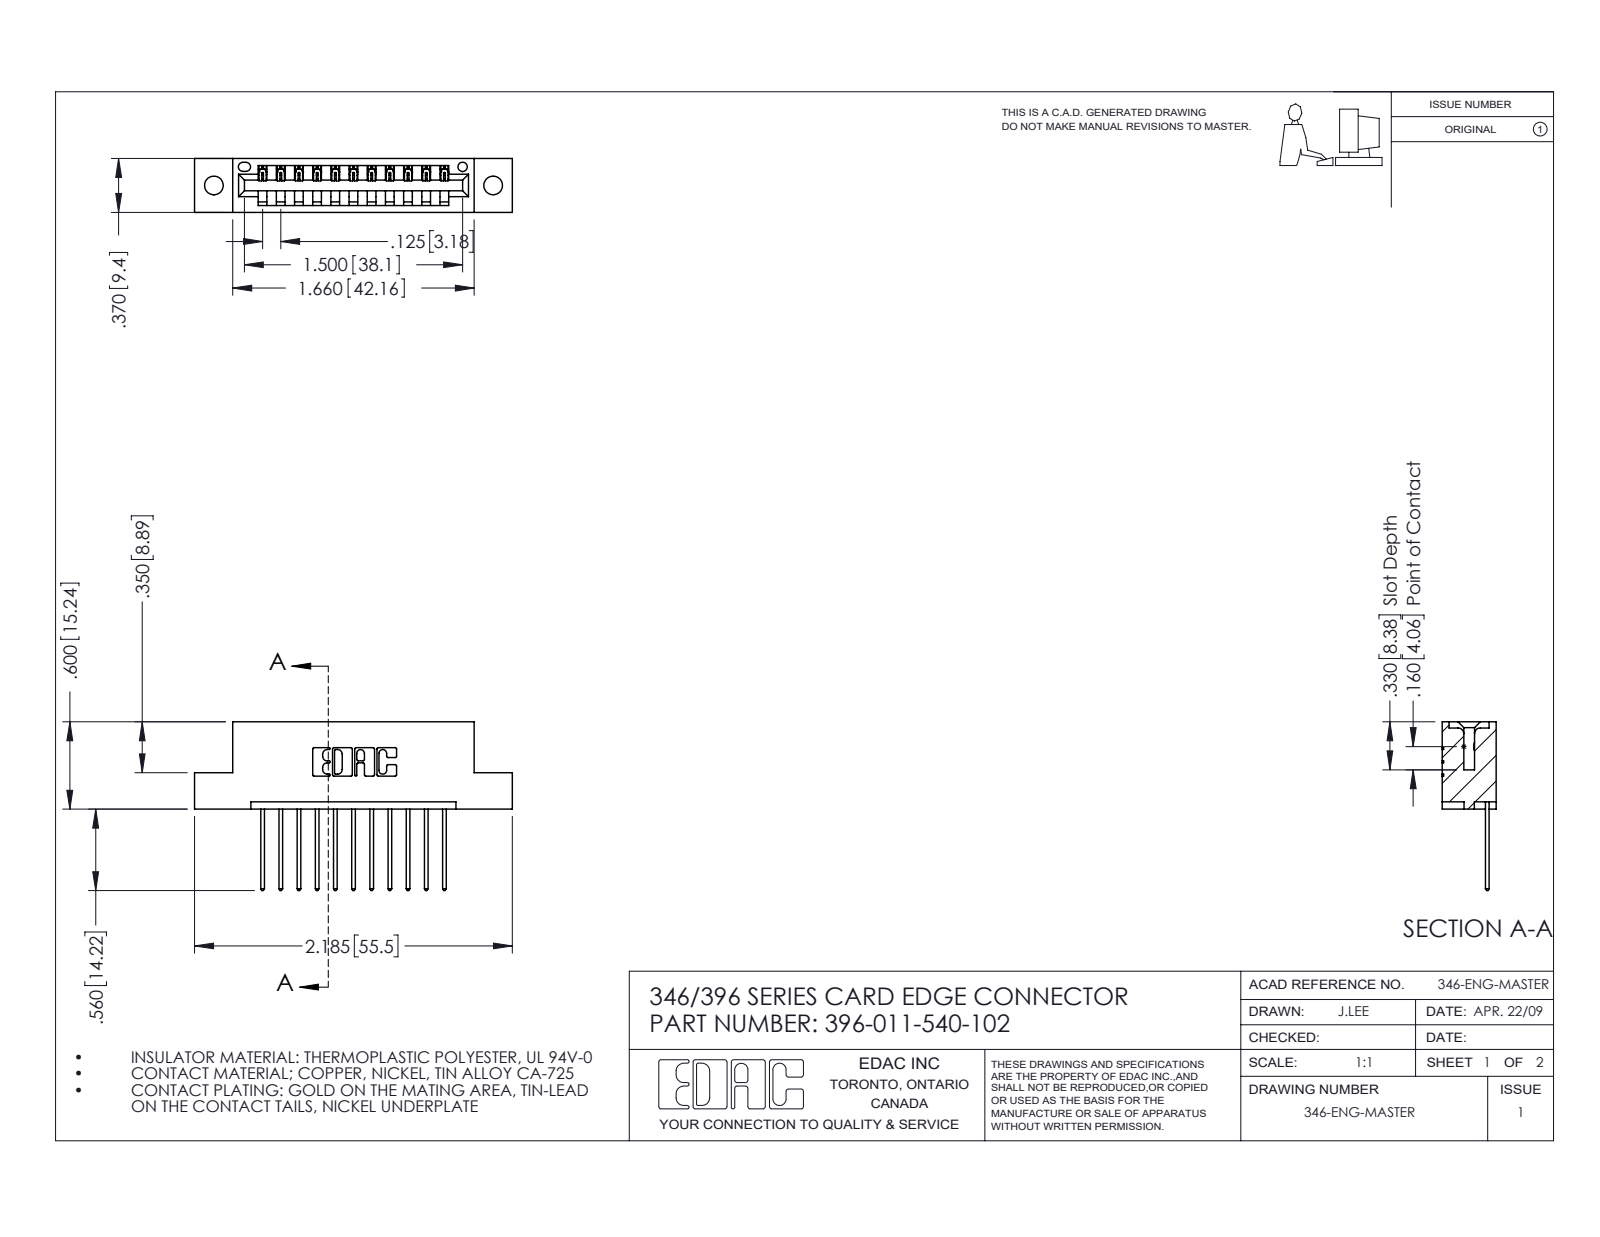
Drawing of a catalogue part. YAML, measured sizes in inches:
part_name: "345-292-001_345-293-140; 346 Part_Flush Mounting Lugs - 0.128 Dia; 396-011-540-102"
step_written_by: "SolidWorks 2016 (CONFIG_CONTROL_DESIGN)"
units: inches
bodies: {solids: 12, faces: 760, planar: 516, cylindrical: 244, other: 0}
overall_size: [2.185, 1.16, 0.37]
volume: 0.31
surface_area: 9.066
round_holes:
  - {diameter: 0.128, count: 2}
  - {diameter: 0.064, count: 1}
partial_cylinders:
  - {radius: 0.006, count: 22}
  - {radius: 0.01, count: 22}
  - {radius: 0.01, count: 22}
  - {radius: 0.007, count: 6}
  - {radius: 0.031, count: 6}
  - {radius: 0.026, count: 3}
  - {radius: 0.031, count: 2}
  - {radius: 0.04, count: 2}
face_to_face_distances: [0.25, 0.048, 0.322, 0.37, 0.072, 0.298, 0.025, 0.148, 0.222, 0.1]
hole_center_spacings: [0.246, 1.715, 1.92]
